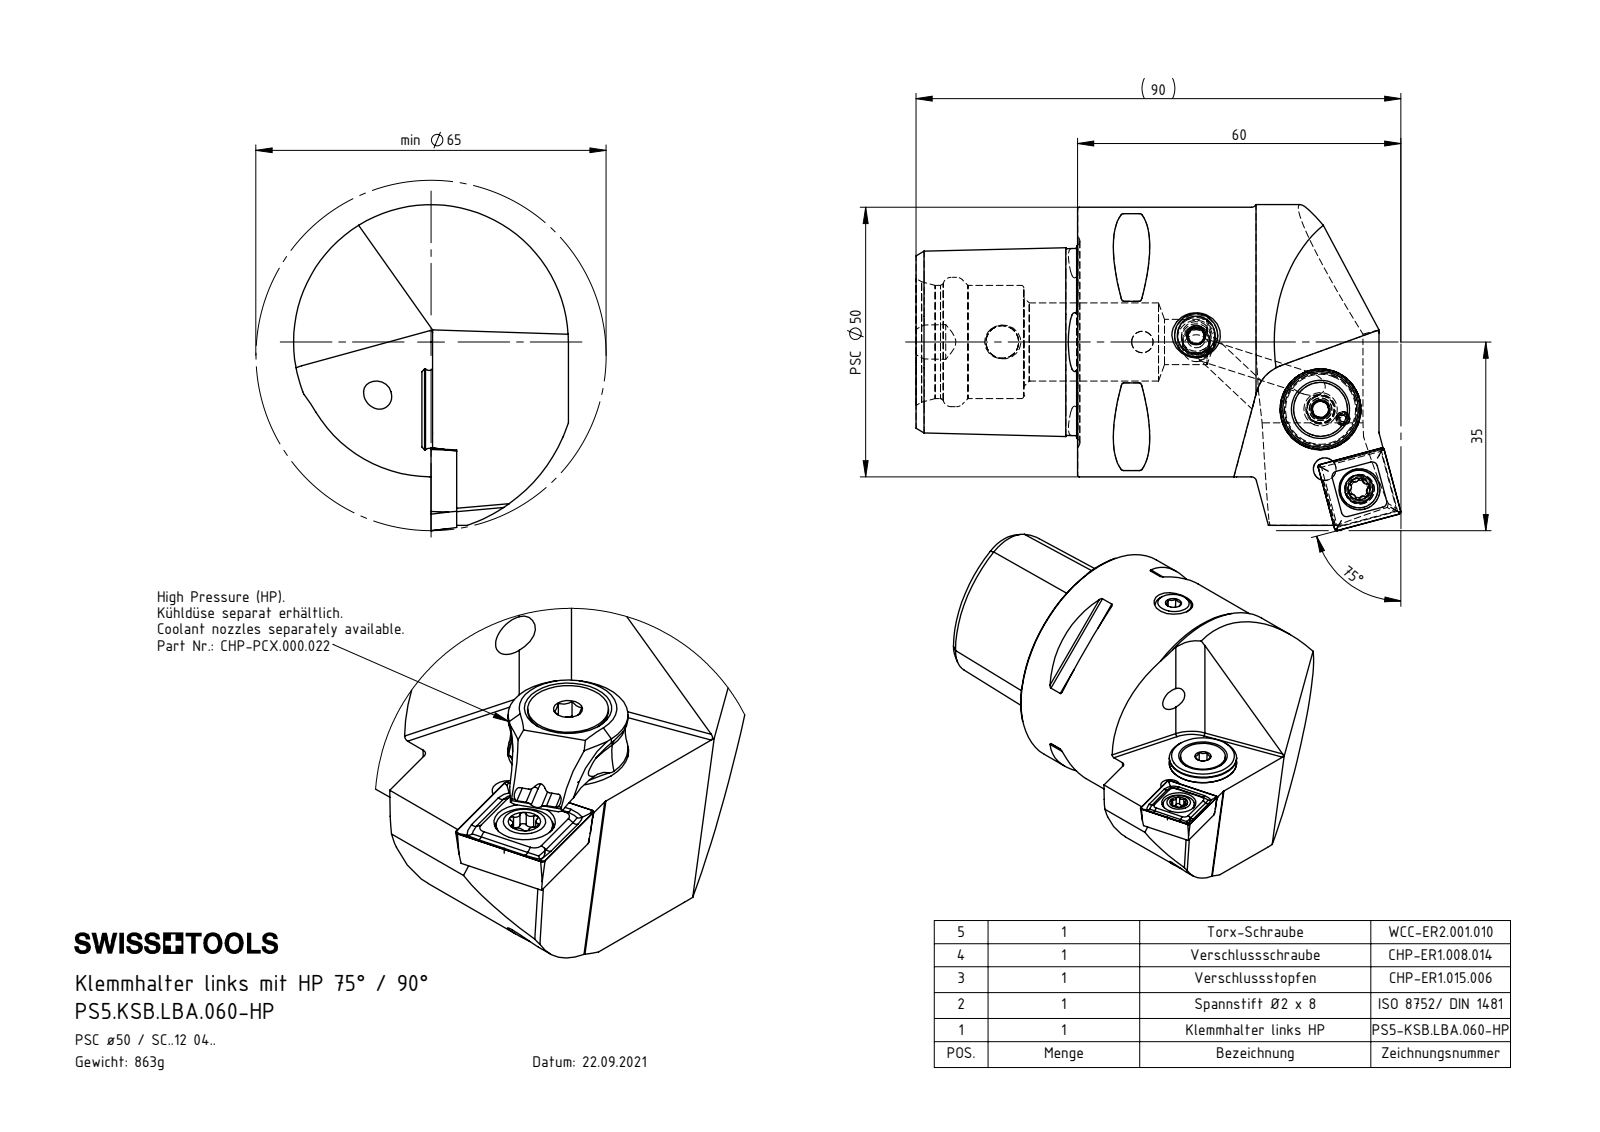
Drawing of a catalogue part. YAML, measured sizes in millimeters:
part_name: "DIN 7991 - M5x18; CHP-ER1.008.014_A; DIN 3771 - 13x1; PS5.KSB.LBA.060-HP (+7 more)"
step_written_by: "SolidWorks 2022 (CONFIG_CONTROL_DESIGN)"
units: millimeters
bodies: {solids: 9, faces: 479, planar: 102, cylindrical: 136, other: 241}
overall_size: [90, 60.5, 51]
volume: 109717
surface_area: 23837
round_holes:
  - {diameter: 4.2, count: 4}
  - {diameter: 5, count: 2}
  - {diameter: 1.2, count: 1}
  - {diameter: 2, count: 1}
  - {diameter: 3, count: 1}
  - {diameter: 4, count: 1}
  - {diameter: 5.3, count: 1}
  - {diameter: 5.5, count: 1}
  - {diameter: 6.1, count: 1}
  - {diameter: 7, count: 1}
  - {diameter: 7.6, count: 1}
  - {diameter: 8.4, count: 1}
round_bosses_or_shafts:
  - {diameter: 5, count: 2}
  - {diameter: 50, count: 1}
  - {diameter: 14.85, count: 1}
  - {diameter: 13.4, count: 1}
  - {diameter: 10, count: 1}
  - {diameter: 8, count: 1}
  - {diameter: 7, count: 1}
  - {diameter: 5.5, count: 1}
partial_cylinders:
  - {radius: 0.5, count: 12}
  - {radius: 1, count: 7}
  - {radius: 0.39, count: 6}
  - {radius: 0.69, count: 6}
  - {radius: 6, count: 3}
  - {radius: 1.1, count: 2}
  - {radius: 1.2, count: 2}
  - {radius: 5, count: 2}
face_to_face_distances: [30, 25.2, 20.74, 4.46, 19.18, 20.7, 4.5, 44.4, 1.5, 3]
hole_center_spacings: [4.5, 7.36, 7.45, 9.97, 11.13, 13.4, 13.46, 16.42]
